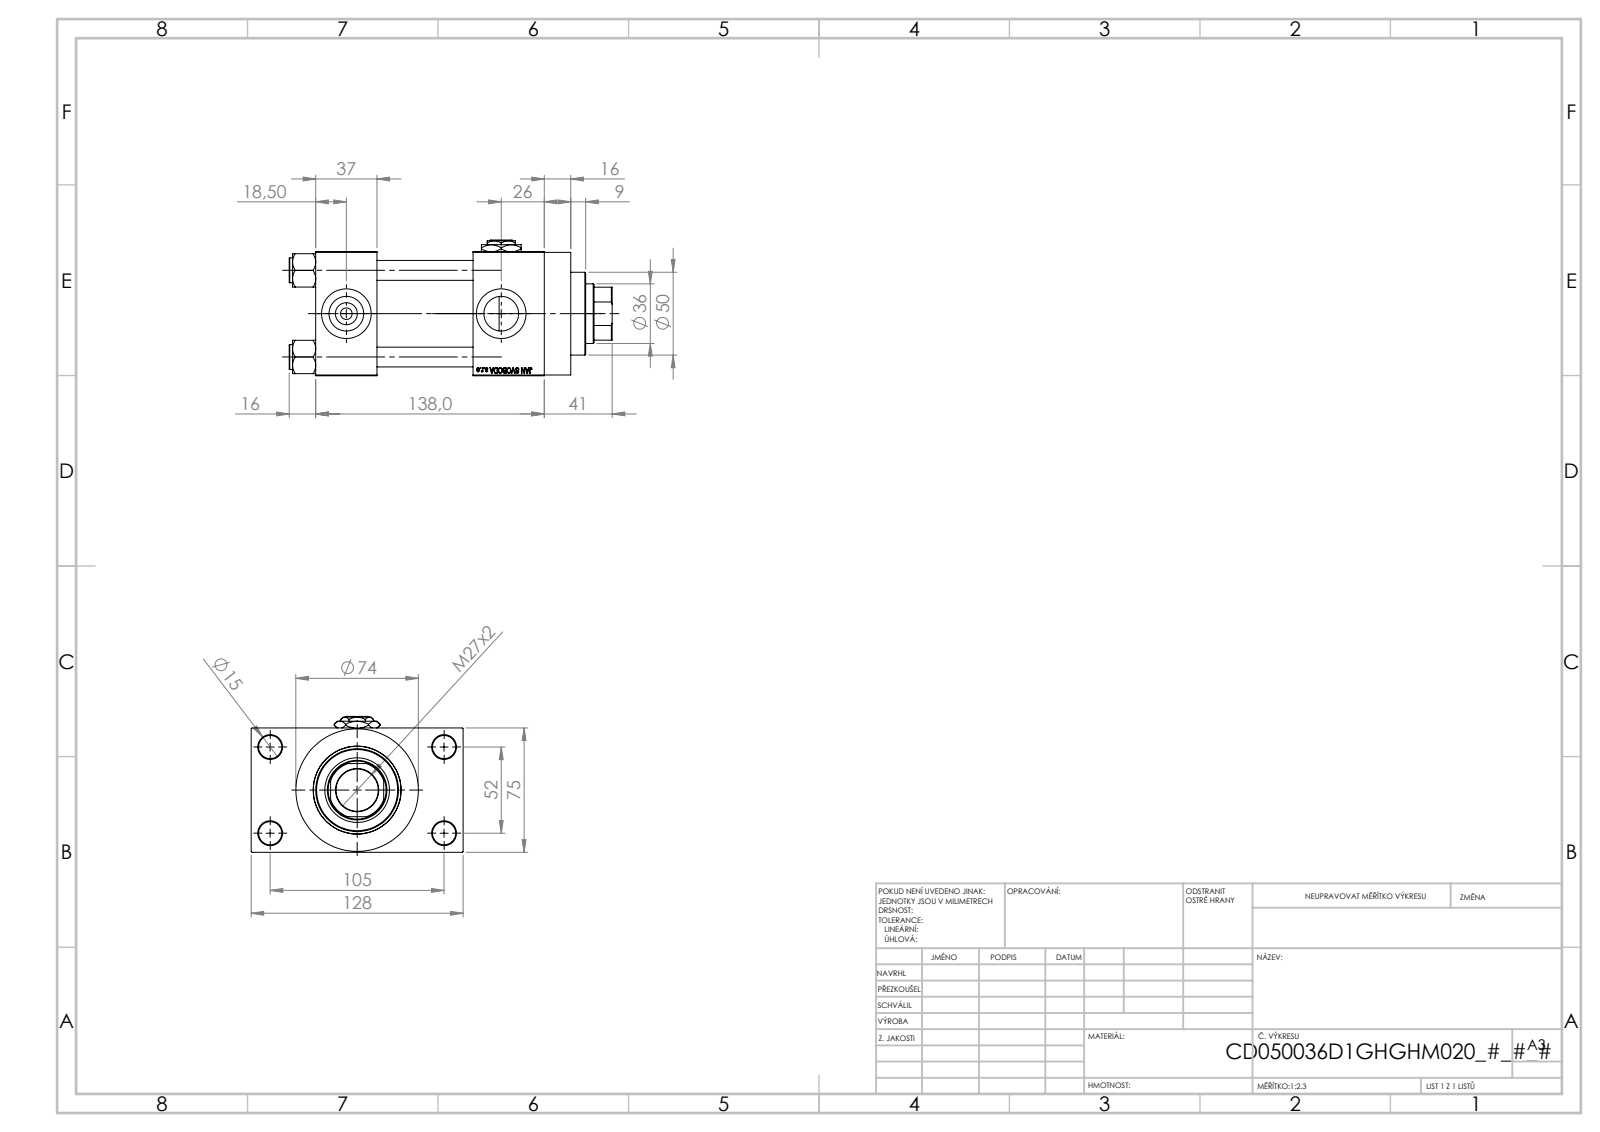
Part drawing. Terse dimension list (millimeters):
name: V215CD_NUT_M5_D; V215CD_D_TYCINKA; V215CD_VCP_D; Zatka_pro_OIL_PORT (+2 more)
written by: SolidWorks 2019 (CONFIG_CONTROL_DESIGN)
unit: mm
bodies: 12 solids, 1151 faces (521 planar, 92 cylindrical, 538 other)
size: 195 × 128 × 82
volume: 815 099 mm³; area: 177 159 mm²
holes: 4× ⌀12, 4× ⌀14, 3× ⌀20.96, 3× ⌀30, 2× ⌀7, 1× ⌀25.5, 1× ⌀36, 1× ⌀39, 1× ⌀41, 1× ⌀53
bosses: 4× ⌀15, 1× ⌀74, 1× ⌀56, 1× ⌀50
rounds: 1× R17.5
face distances: 75, 58, 37, 95, 26.5, 138, 43, 101, 101.5, 16
hole spacings: 26.35, 36.98, 52.3, 58.43, 58.59, 78.65, 94.37, 52
